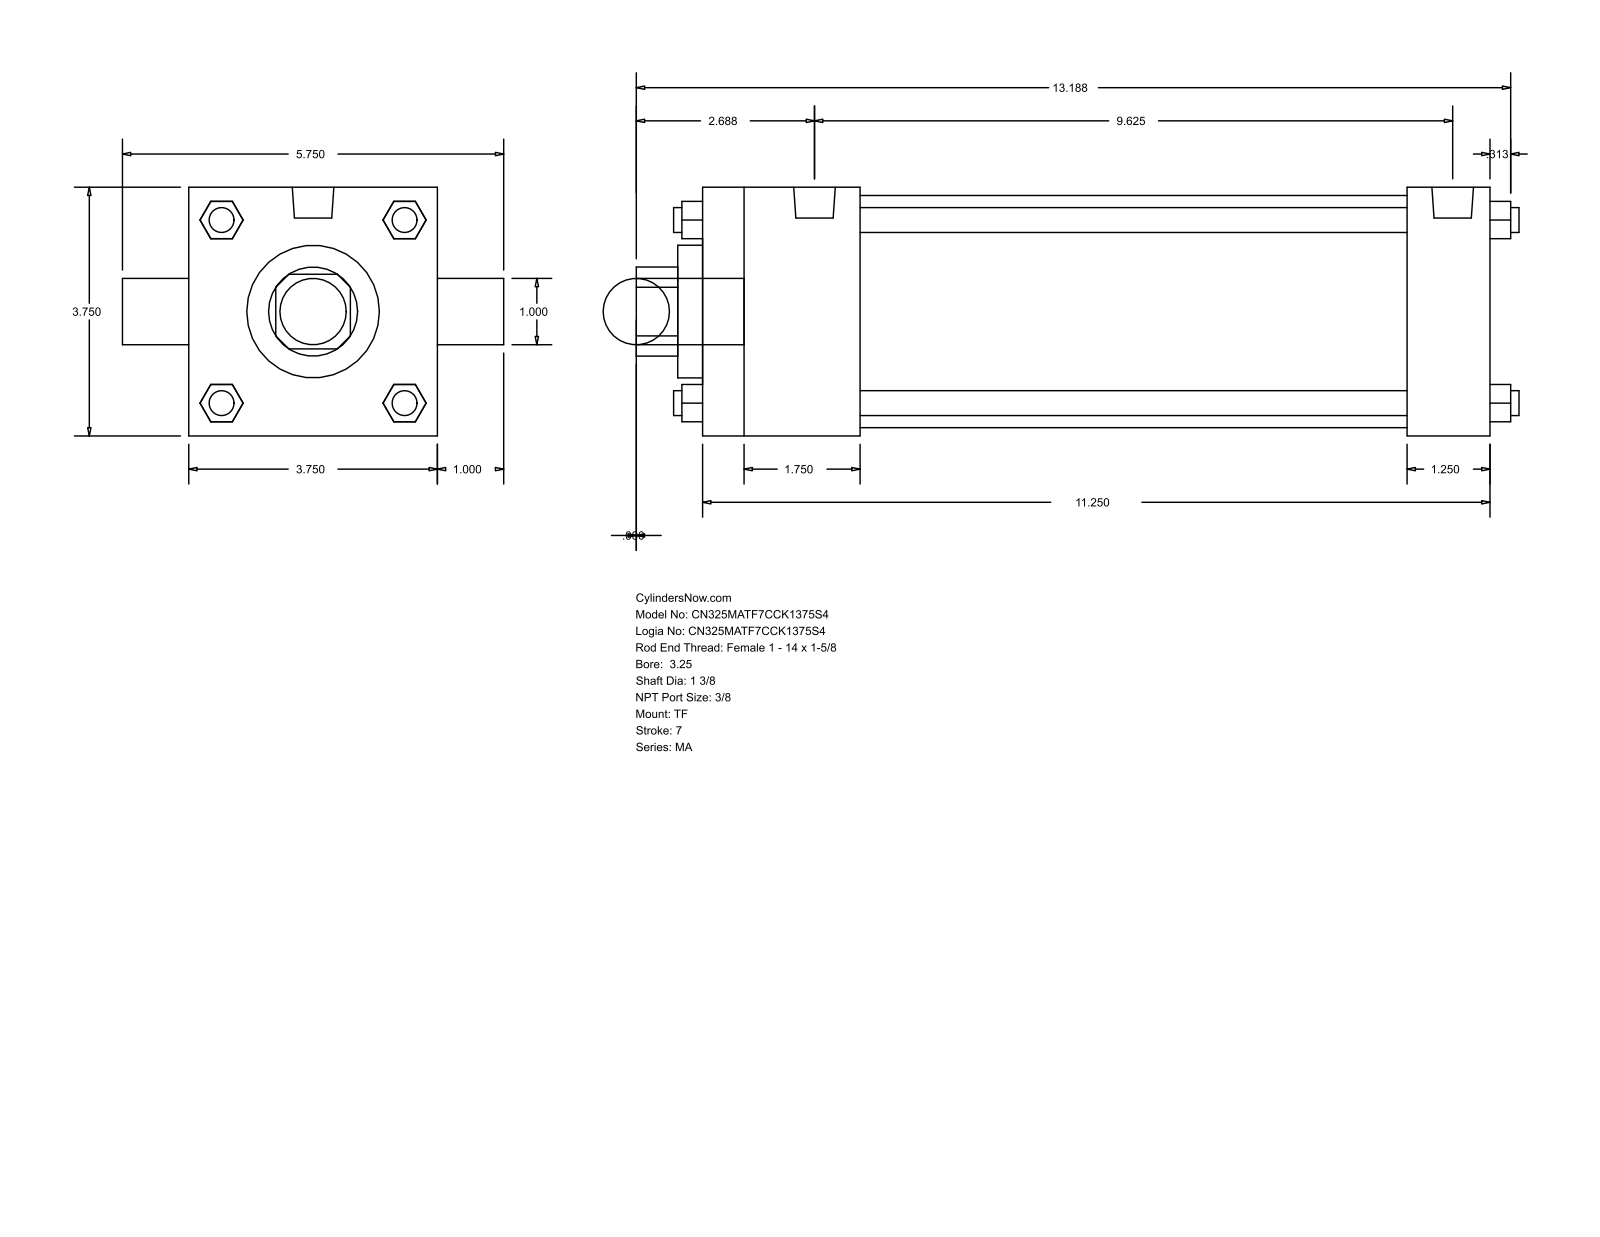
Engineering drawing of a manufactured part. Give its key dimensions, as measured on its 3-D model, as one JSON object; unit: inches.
{"part_name": "MA_TF__0325_1.375", "step_written_by": "GSSL Pune (CONFIG_CONTROL_DESIGN)", "units": "inches", "bodies": {"solids": 0, "faces": 120, "planar": 92, "cylindrical": 28, "other": 0}, "overall_size": [13.313, 5.75, 3.75], "round_holes": [[1, 1], [1.375, 1], [2, 1], [3.5, 1]], "round_bosses_or_shafts": [[0.375, 4], [0.437, 3], [0.627, 2], [1, 1]], "partial_cylinders_radius": [[0.672, 1]], "face_to_face_distances": [3.75, 11.875, 2.375, 10.625, 8.25, 9.5, 1.25, 0.375, 2.75, 11]}
